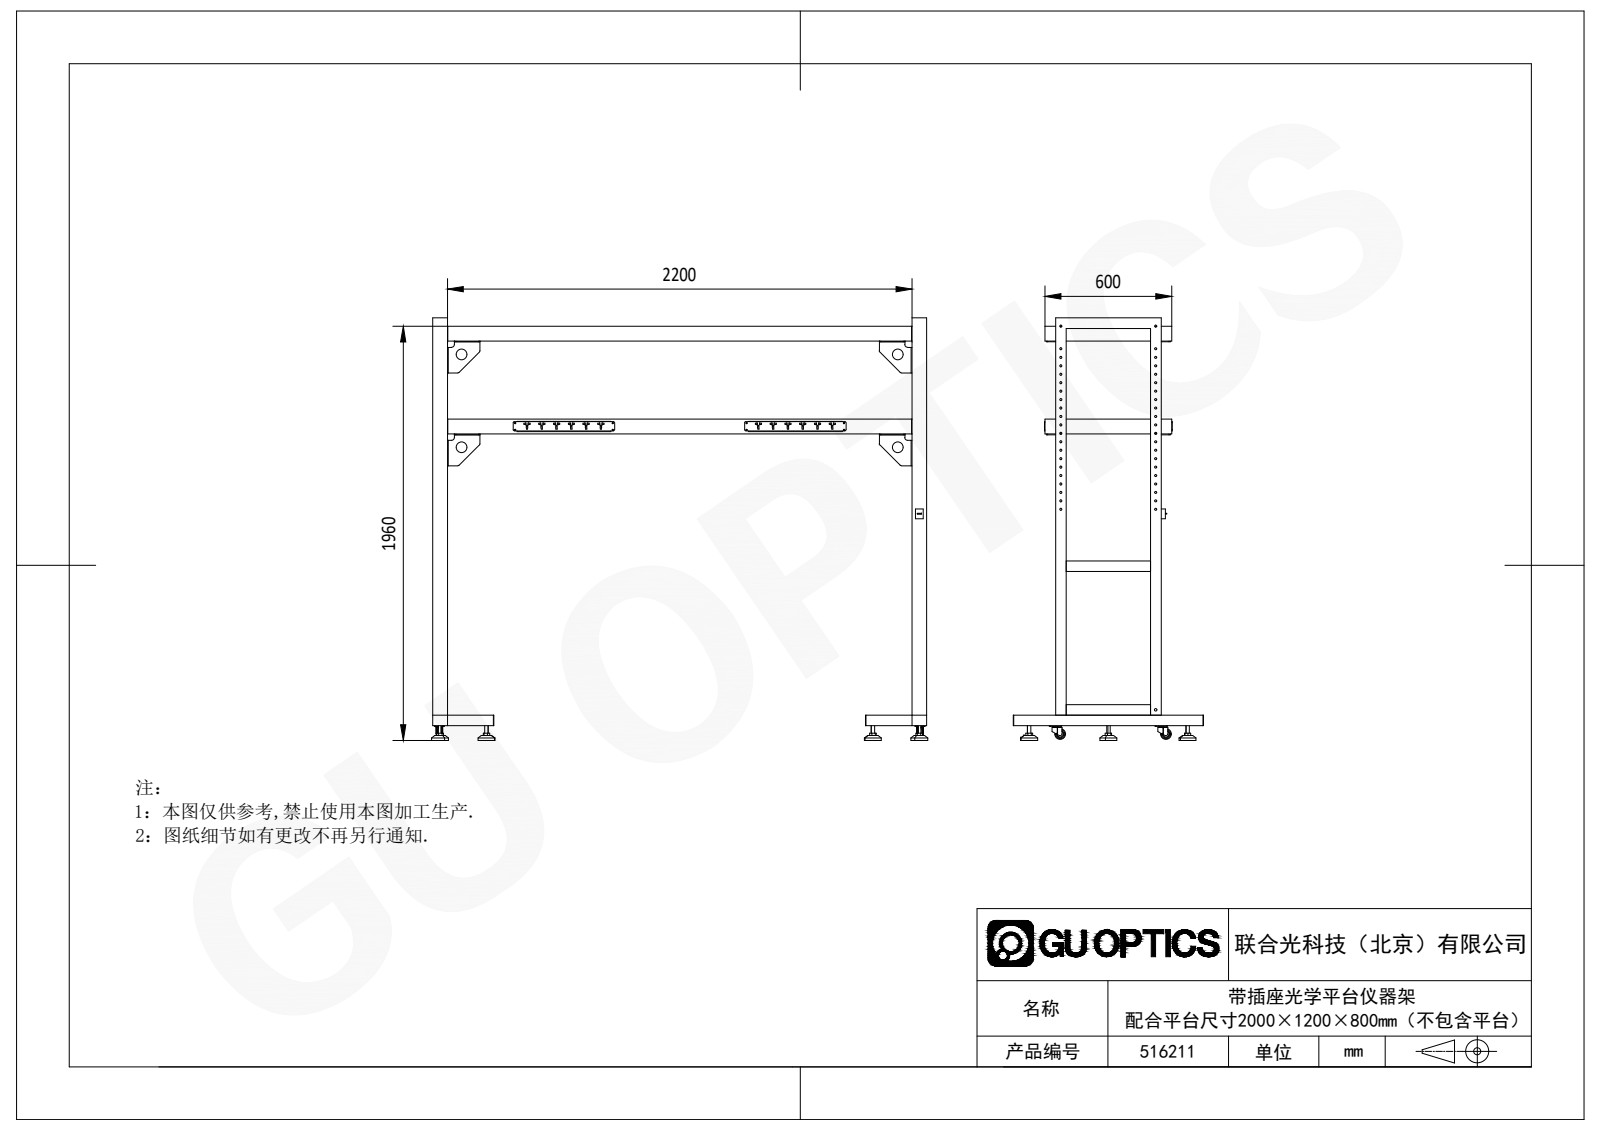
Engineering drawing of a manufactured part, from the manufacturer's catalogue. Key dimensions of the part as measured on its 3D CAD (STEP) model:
Part name (STEP PRODUCT): 516211
STEP written by: SolidWorks 2020 (CONFIG_CONTROL_DESIGN)
Units: millimetres
Bodies: 59 solids, 2591 faces (1443 planar, 1072 cylindrical, 76 other)
Overall size (bounding box): 2350 × 2001 × 900
Volume: 23 540 000 mm³ · Surface area: 16 710 000 mm²
Round holes (diameter × count): ⌀9 ×66, ⌀6.1 ×16, ⌀10 ×16, ⌀6.5 ×12, ⌀4.2 ×8, ⌀5.2 ×8, ⌀6 ×8, ⌀17 ×6, ⌀18 ×6, ⌀26 ×6, ⌀69 ×6, ⌀3.2 ×4
Round bosses / shafts (diameter × count): ⌀80 ×6, ⌀16 ×6, ⌀26 ×4, ⌀18 ×4, ⌀50 ×2, ⌀10 ×2
Partial cylindrical surfaces — rounded edges, fillets, slot ends (radius × count): R5 ×36, R7 ×24, R3 ×16, R4.25 ×12, R1.5 ×8, R1.51 ×8, R4.01 ×8, R13 ×4
Main face-to-face distances: 440, 1.5, 3, 70, 2, 50, 67, 2.5, 438.5, 67.5
Hole centre spacings: 40, 80, 120, 280, 160, 200, 240, 320
